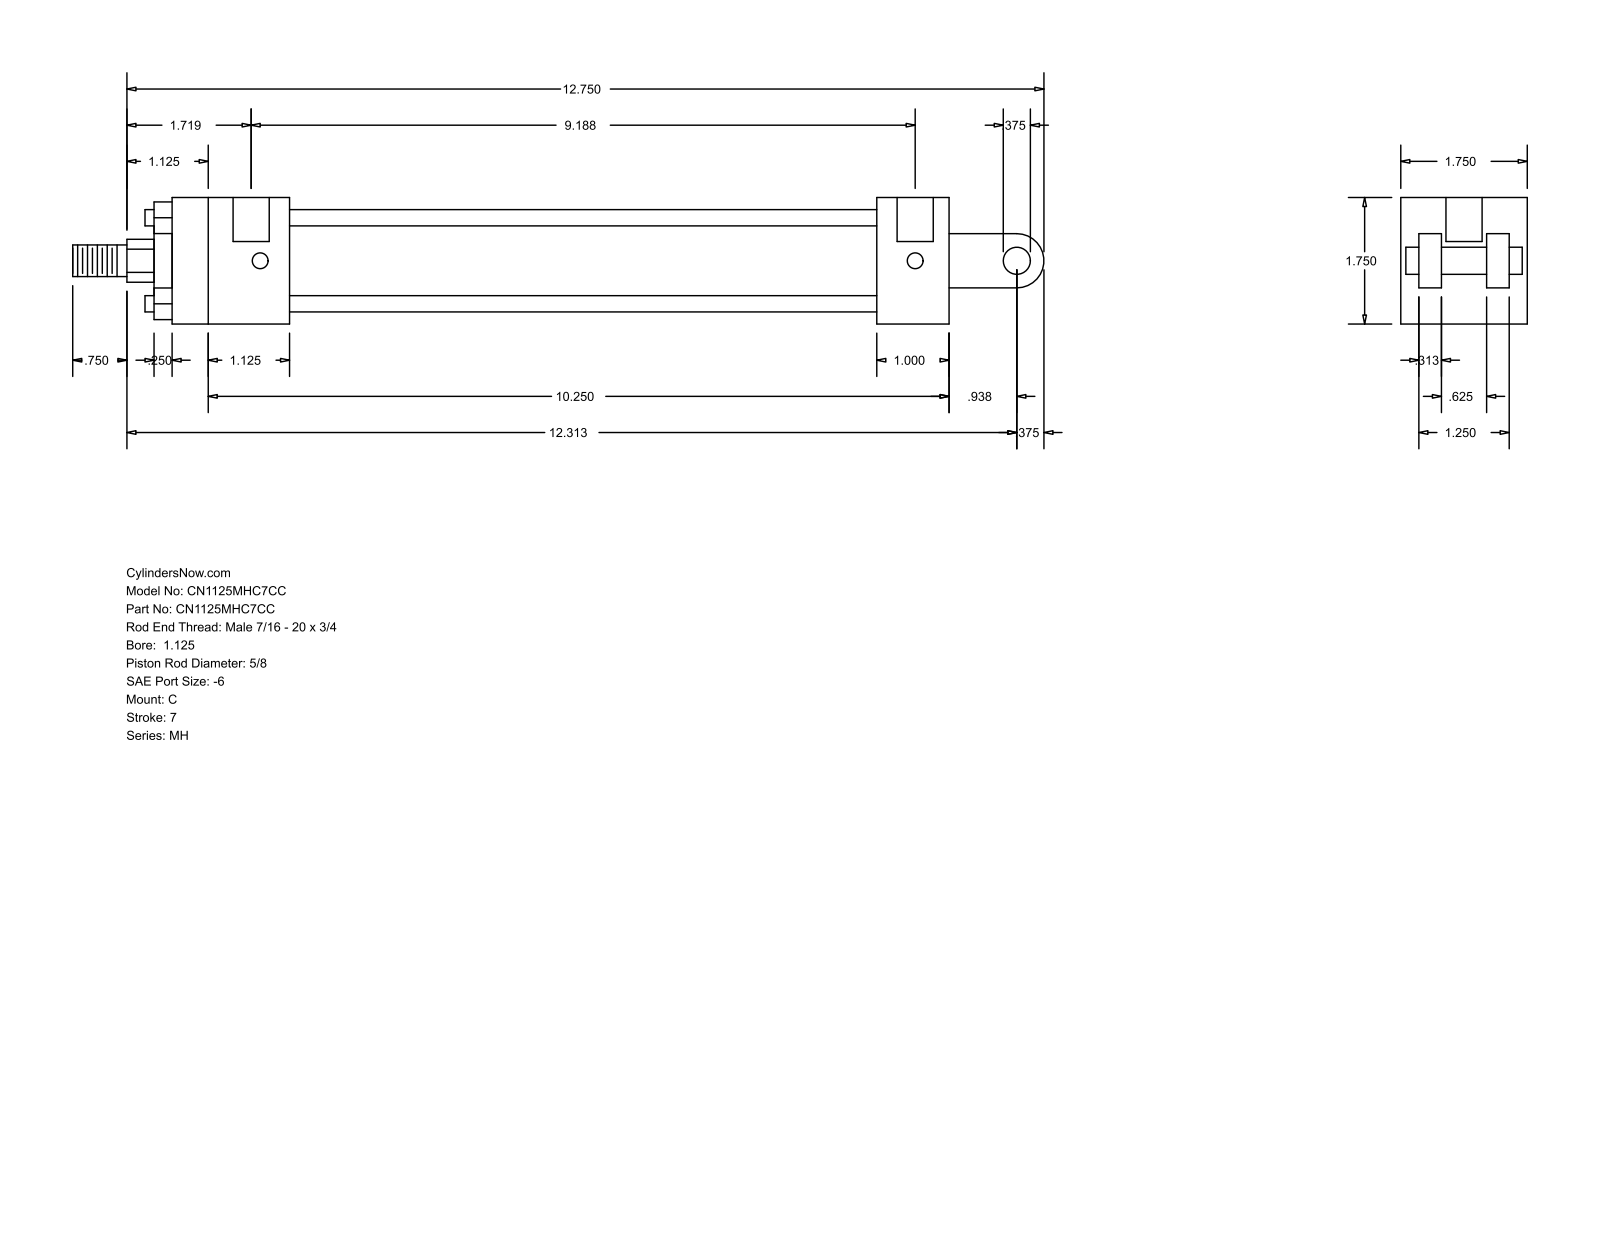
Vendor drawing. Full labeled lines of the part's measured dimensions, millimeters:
Part name (STEP PRODUCT): MH_C__0112_0.625
STEP written by: GSSL Pune (CONFIG_CONTROL_DESIGN)
Units: millimetres
Bodies: 0 solids, 99 faces (70 planar, 29 cylindrical, 0 other)
Overall size (bounding box): 341.31 × 44.45 × 44.45
Round holes (diameter × count): ⌀5.56 ×4, ⌀12.7 ×2
Round bosses / shafts (diameter × count): ⌀5.71 ×4, ⌀34.92 ×1, ⌀28.57 ×1, ⌀15.88 ×1, ⌀11.11 ×1, ⌀9.53 ×1
Partial cylindrical surfaces — rounded edges, fillets, slot ends (radius × count): R7.54 ×1, R9.53 ×1
Main face-to-face distances: 44.46, 6.35, 31.76, 14.29, 30.17, 38.11, 7.94, 23.82, 12.7, 41.27
Hole centre spacings: 230.19, 3.17, 233.36
